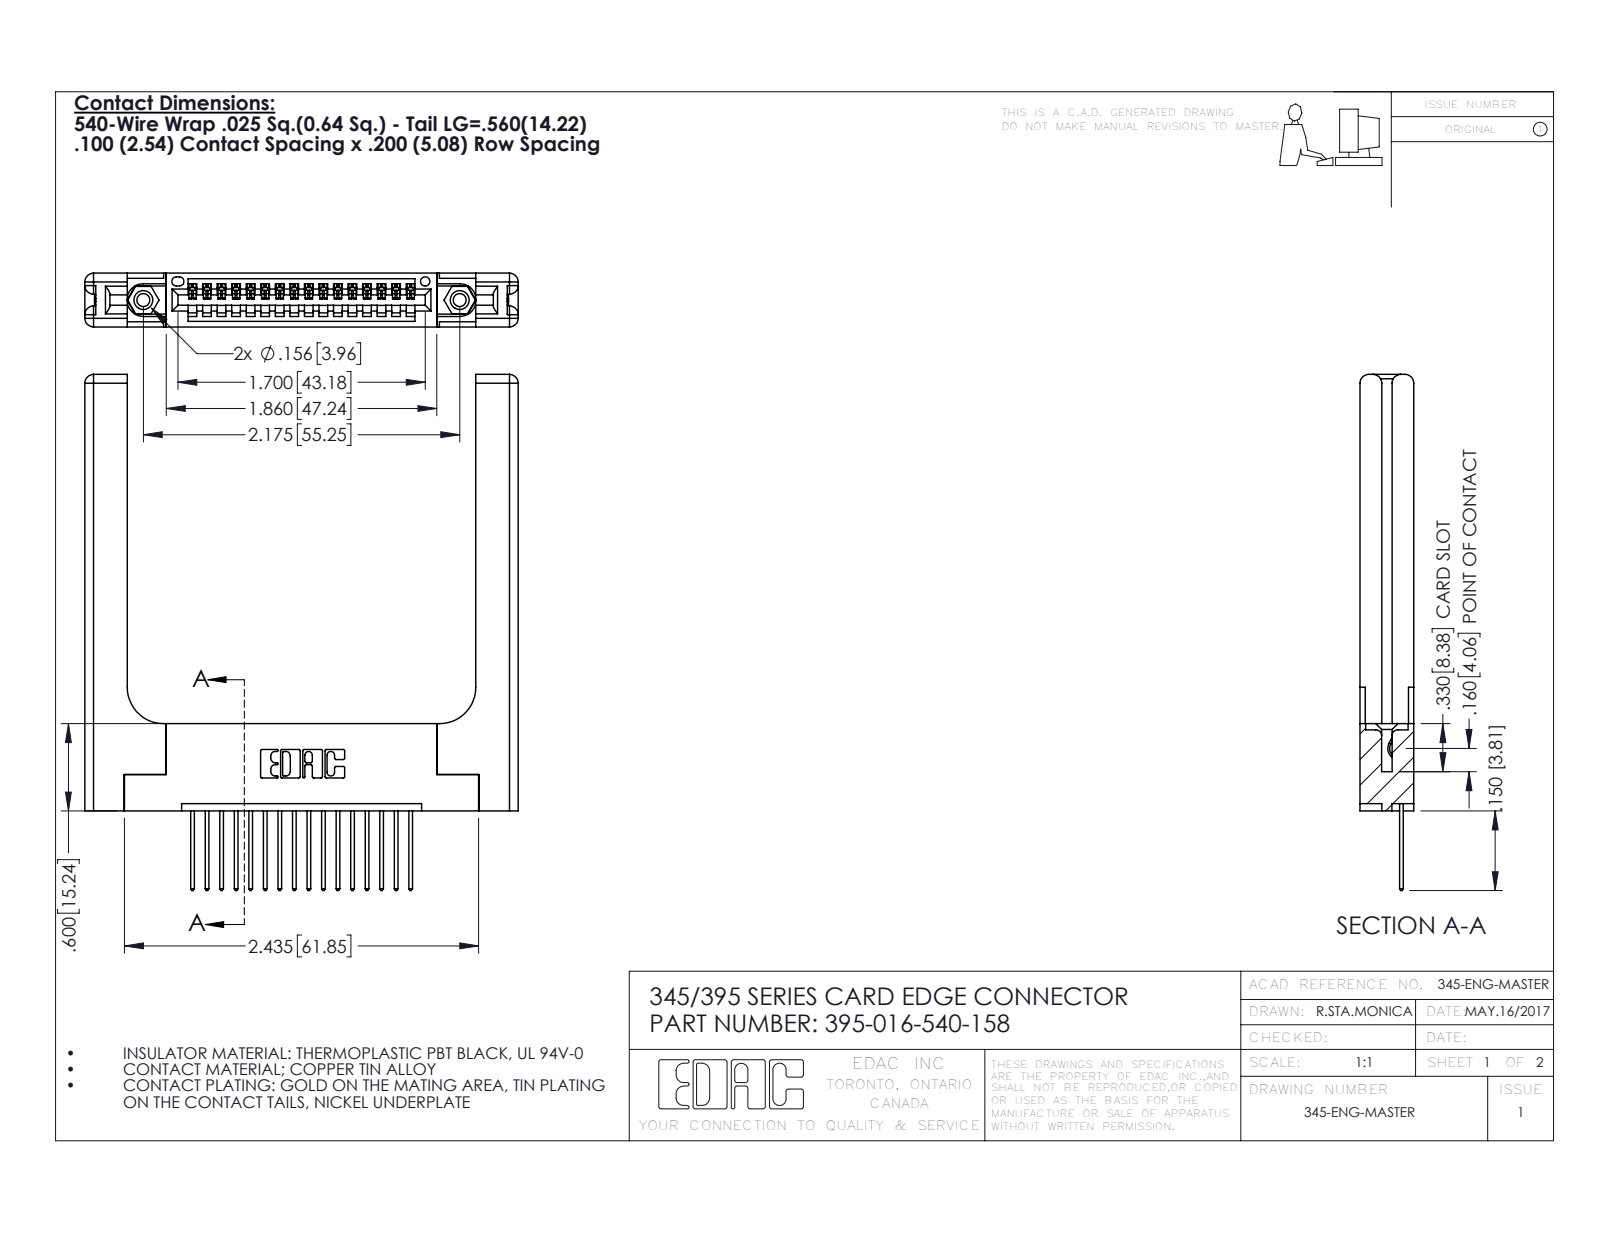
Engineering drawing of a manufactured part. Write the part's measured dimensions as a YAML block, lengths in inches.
part_name: "395-016-540-158; 345-250-001_345-250-001-102; 345-292-001_345-293-140; 345-220-058_345-220-058 (+1 more)"
step_written_by: "SolidWorks 2016 (CONFIG_CONTROL_DESIGN)"
units: inches
bodies: {solids: 21, faces: 1310, planar: 868, cylindrical: 382, other: 60}
overall_size: [3.547, 2.979, 0.37]
volume: 0.946
surface_area: 22.33
round_holes:
  - {diameter: 0.089, count: 2}
  - {diameter: 0.125, count: 2}
  - {diameter: 0.156, count: 2}
  - {diameter: 0.064, count: 1}
round_bosses_or_shafts:
  - {diameter: 0.155, count: 2}
partial_cylinders:
  - {radius: 0.006, count: 32}
  - {radius: 0.01, count: 32}
  - {radius: 0.01, count: 22}
  - {radius: 0.06, count: 16}
  - {radius: 0.007, count: 6}
  - {radius: 0.031, count: 6}
  - {radius: 0.026, count: 3}
  - {radius: 0.03, count: 2}
face_to_face_distances: [0.37, 0.072, 0.298, 0.15, 0.077, 0.148, 0.2, 0.22, 0.098, 0.272]
hole_center_spacings: [0.27, 1.942, 2.175]
